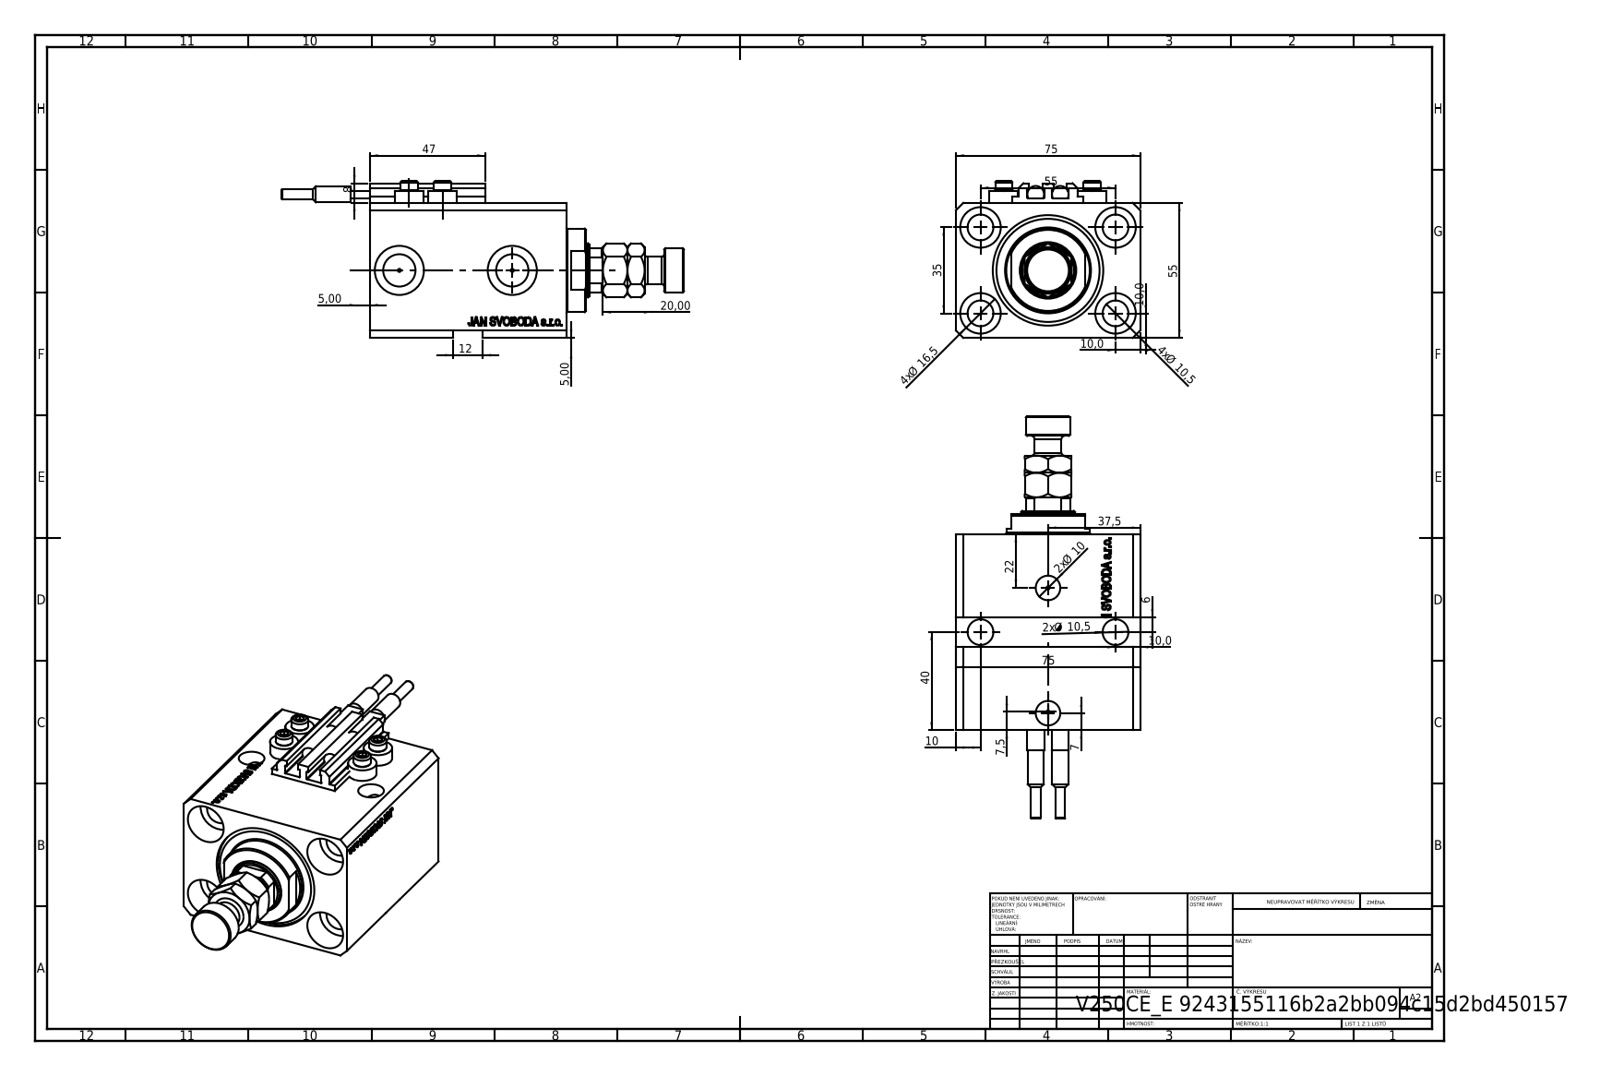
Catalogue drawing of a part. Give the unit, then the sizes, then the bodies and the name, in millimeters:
Units: millimetres
Overall size (bounding box): 163.9 × 75 × 64
Round holes (diameter × count): ⌀10.5 ×7, ⌀1.25 ×4, ⌀4 ×4, ⌀16.5 ×4, ⌀10 ×2, ⌀13.16 ×2, ⌀20 ×2, ⌀22 ×1, ⌀32 ×1, ⌀45 ×1
Round bosses / shafts (diameter × count): ⌀11.6 ×4, ⌀7 ×4, ⌀6.8 ×2, ⌀6.5 ×2, ⌀4 ×2, ⌀34 ×1, ⌀18 ×1, ⌀11 ×1
Partial cylindrical surfaces — rounded edges, fillets, slot ends (radius × count): R0.2 ×10, R10.5 ×1
Main face-to-face distances: 55, 75, 3, 80, 52.9, 27.1, 9.9, 57, 43, 70.1
Hole centre spacings: 32.6, 55, 13.6, 14.09, 19.89, 20.12, 25.81, 28.48
Volume: 295 513 mm³ · Surface area: 82 514 mm²
Bodies: 11 solids, 1168 faces (562 planar, 142 cylindrical, 464 other)
Part name (STEP PRODUCT): SWITCH_V250CE; V250CE_VC_E; MFA; V250CE_E_Body (+2 more)
STEP written by: SolidWorks 2019 (CONFIG_CONTROL_DESIGN)
